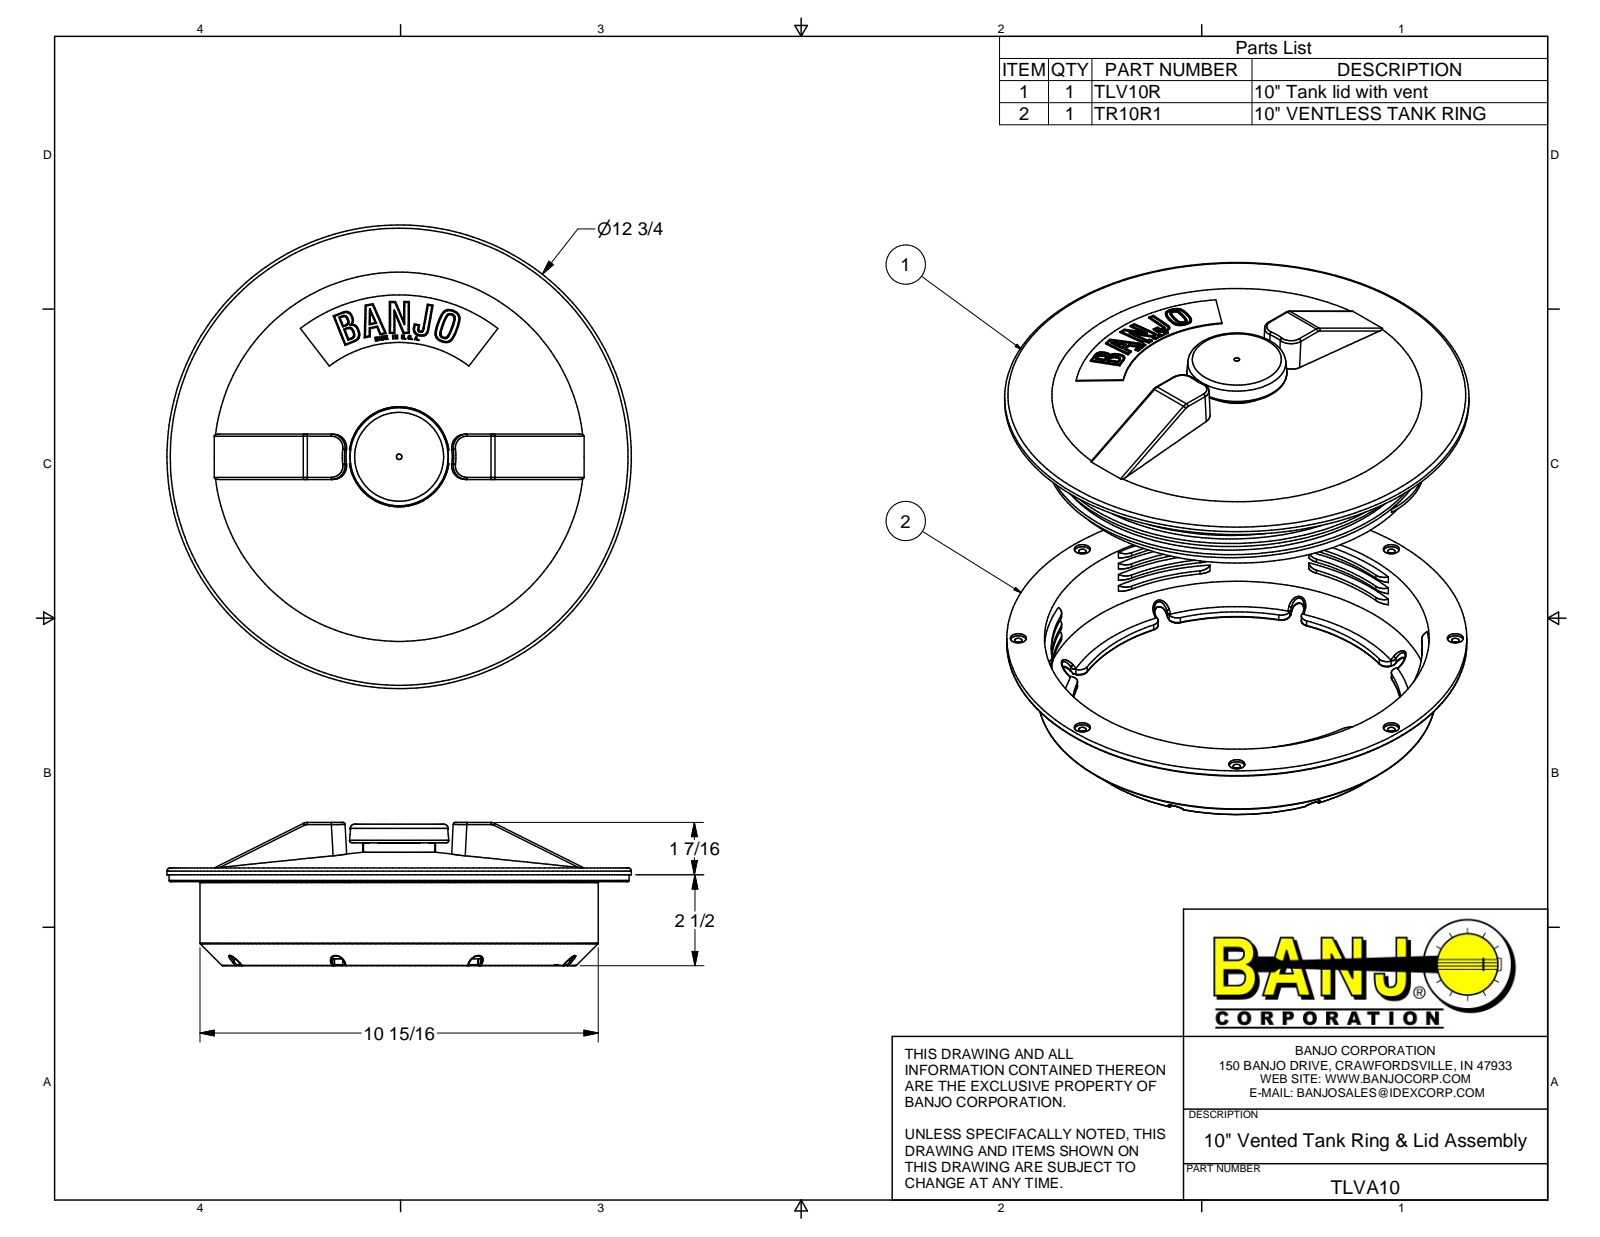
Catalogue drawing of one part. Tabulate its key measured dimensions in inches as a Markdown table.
| quantity | value |
| --- | --- |
| part name | TR10R1; TLV2; TL10r1; TLV1 (+2 more) |
| STEP written by | Autodesk Inventor 2016 (AUTOMOTIVE_DESIGN) |
| units | inches |
| bodies | 4 solids, 810 faces (303 planar, 194 cylindrical, 313 other) |
| overall size | 12.75 × 12.75 × 3.941 |
| volume | 74.63 in³ |
| surface area | 775.4 in² |
| round holes (diameter × count) | 0.203 × 8, 0.438 × 8, 1.76 × 1, 2.24 × 1, 9.775 × 1, 10.562 × 1 |
| round bosses / shafts (diameter × count) | 12.75 × 1, 12.63 × 1, 10.938 × 1, 10.5 × 1, 10.155 × 1, 3 × 1, 2.5 × 1, 2.22 × 1 |
| partial cylindrical surfaces (radius × count) | 0.06 × 18, 0.03 × 16, 0.25 × 16, 0.375 × 16, 0.178 × 8, 0.188 × 4, 2.711 × 4, 0.248 × 2 |
| main face-to-face distances | 0.19, 0.378, 0.187, 0.125, 2.691, 2.501, 2.314, 1.377, 1.187, 0.999 |
| hole center spacings | 4.592, 6, 11.086, 8.485, 8.485, 12, 12 |
